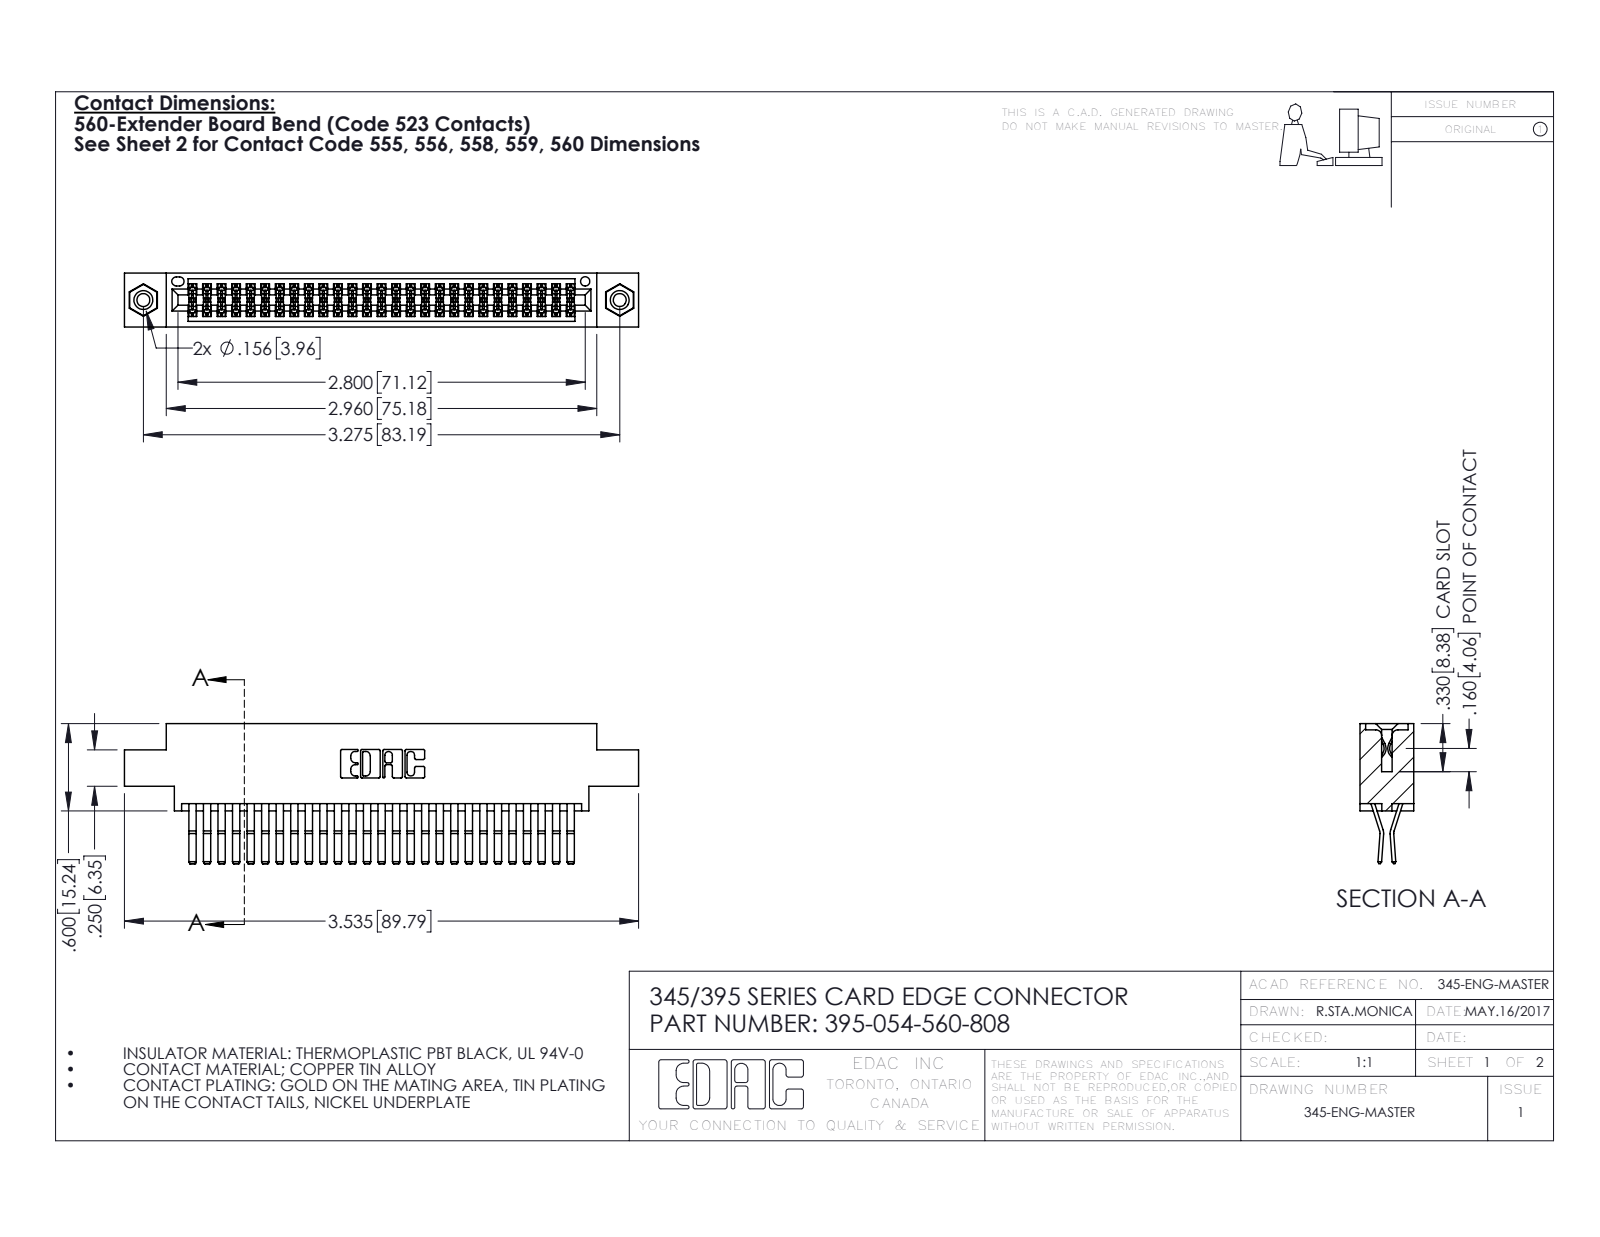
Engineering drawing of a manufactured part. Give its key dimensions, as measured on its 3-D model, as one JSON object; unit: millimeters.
{"part_name": "345 Part_0.170 Offset - 0.156 Dia-TI; 395-054-560-808; 345-250-001_345-250-003-102; 345-292-001_560 Tail", "step_written_by": "SolidWorks 2016 (CONFIG_CONTROL_DESIGN)", "units": "millimeters", "bodies": {"solids": 57, "faces": 2998, "planar": 1898, "cylindrical": 1084, "other": 16}, "overall_size": [89.8, 24.4, 9.4], "volume_mm3": 8820, "surface_area_mm2": 13810, "round_holes": [[2.3, 2], [3.2, 2], [4, 2], [1.6, 1]], "round_bosses_or_shafts": [[3.9, 2]], "partial_cylinders_radius": [[0.2, 81], [0.3, 22], [0.2, 6], [0.8, 6], [0.7, 3], [0.3, 2], [0.4, 2], [0.5, 2]], "face_to_face_distances": [0.6, 1.8, 7.6, 9.4, 5.1, 2.5, 6.9, 5.7, 4.4, 3.8], "hole_center_spacings": [6.9, 77.2, 83.2]}
